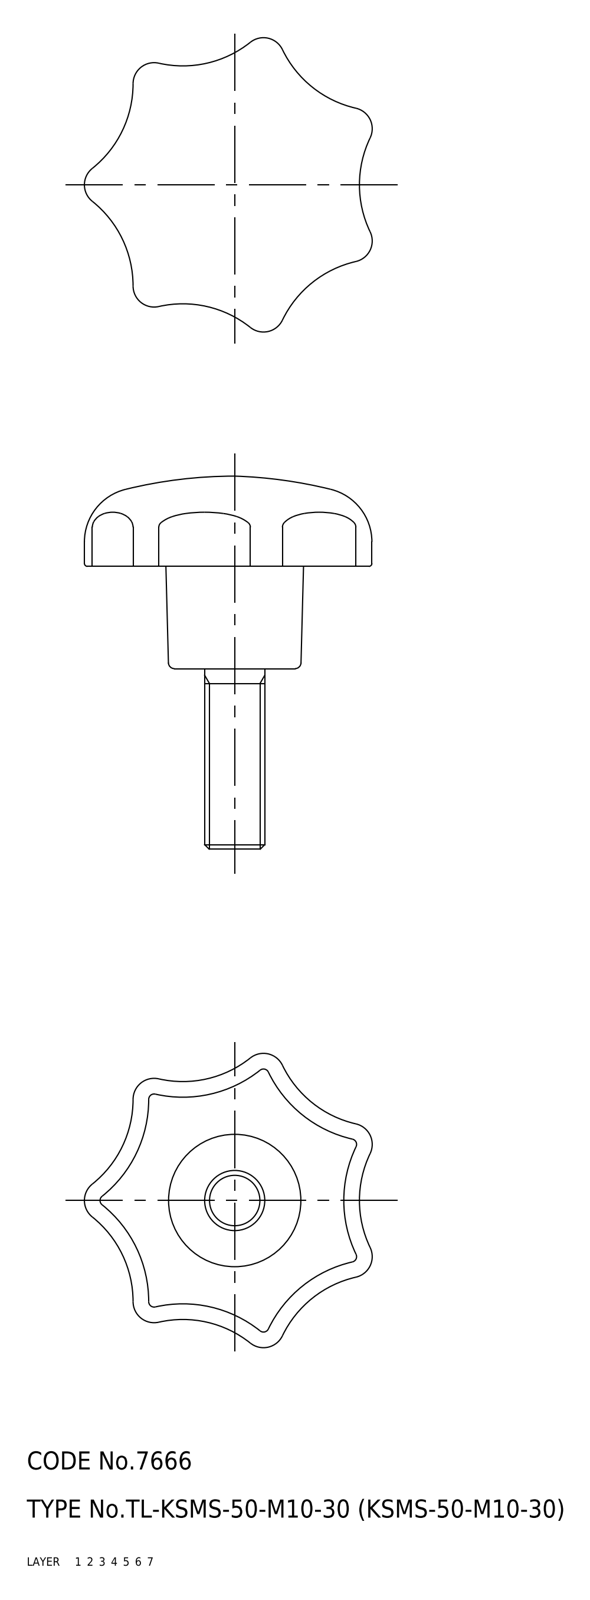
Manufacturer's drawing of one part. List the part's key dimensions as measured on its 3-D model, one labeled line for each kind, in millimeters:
Part name (STEP PRODUCT): 67117884; 67117897
STEP written by: CADfix (AUTOMOTIVE_DESIGN)
Units: millimetres
Bodies: 2 solids, 89 faces (0 planar, 0 cylindrical, 89 other)
Overall size (bounding box): 62 × 48.92 × 47.87
Volume: 21 483 mm³ · Surface area: 10 501 mm²
